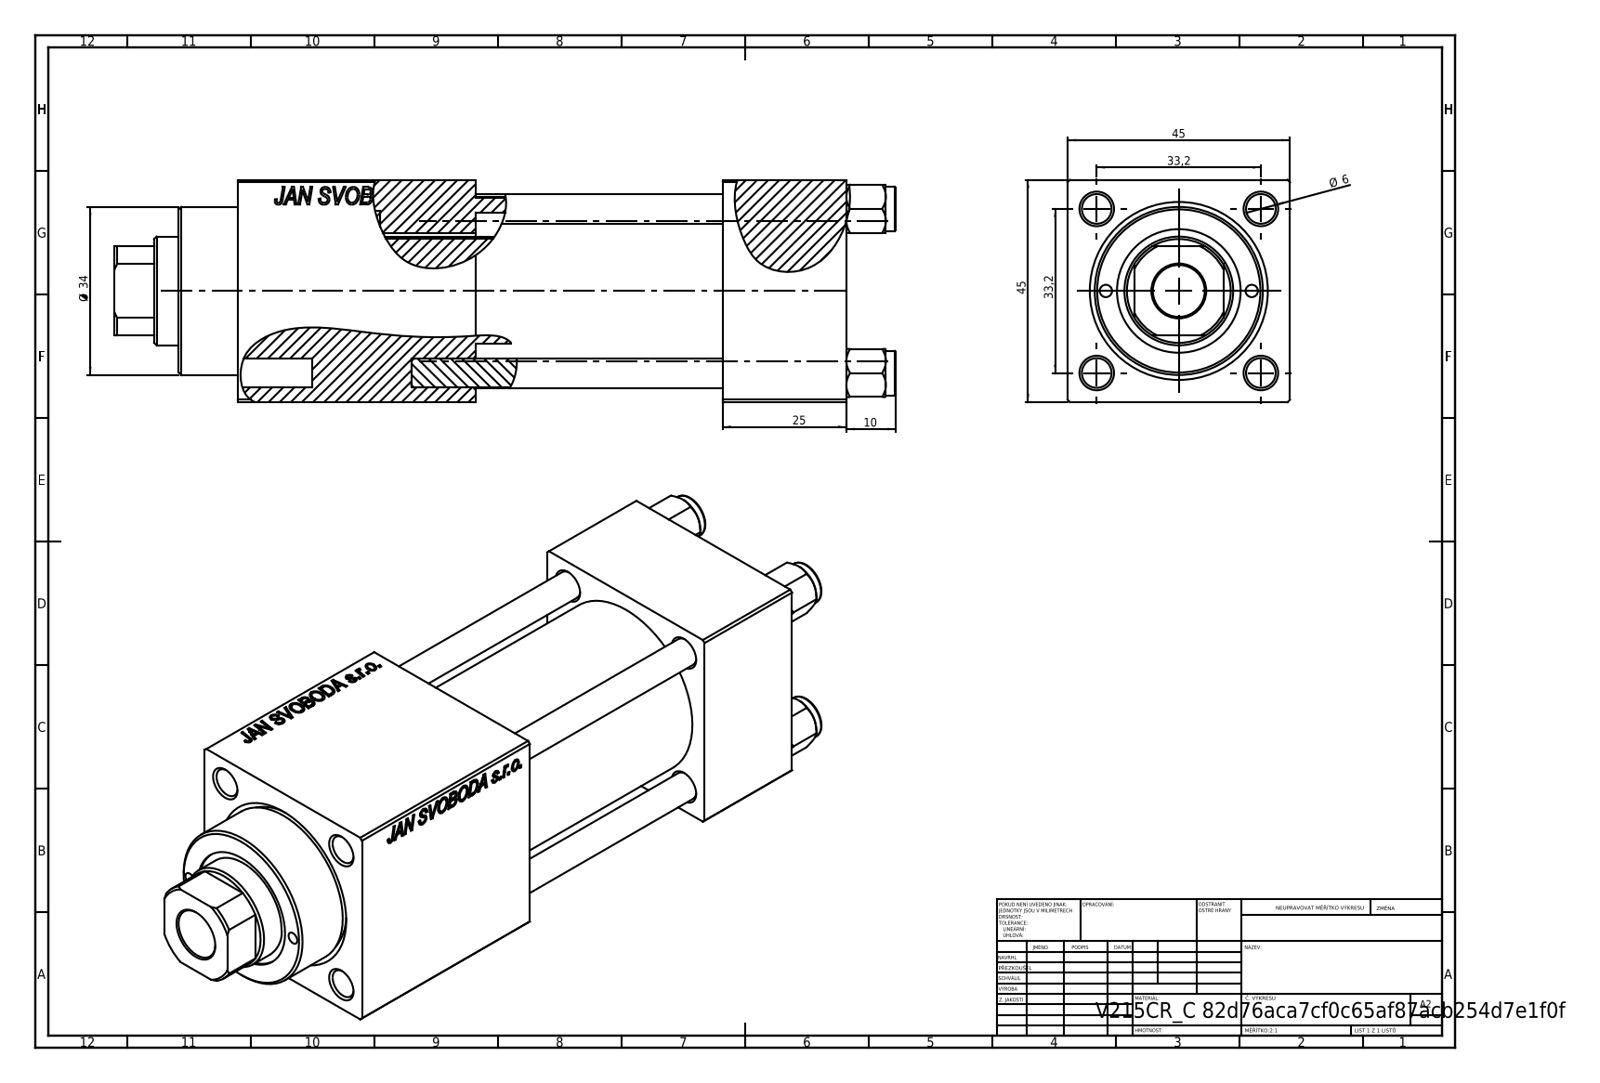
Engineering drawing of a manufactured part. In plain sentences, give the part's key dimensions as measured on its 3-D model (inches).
The part is named "NUT_M5_C; V215CR_C_TYCINKA; V215CR_VCP_C; V215_VC_A (+1 more)". Its 3-D file was written by "SolidWorks 2019 (CONFIG_CONTROL_DESIGN)". It is 11 solids with 1153 faces: 527 planar, 90 cylindrical and 536 other. Overall it measures 6.22 by 1.772 by 1.772 inches. Its volume is 12.8 cubic inches and its surface area 110.9 square inches. Round holes: 4 of diameter 0.236, 2 of diameter 0.098, 2 of diameter 0.276, 2 of diameter 0.518, 2 of diameter 0.787, 1 of diameter 0.413, 1 of diameter 0.866, 1 of diameter 0.945, 1 of diameter 0.984, 1 of diameter 1.26, 1 of diameter 1.299. Round bosses or shafts: 4 of diameter 0.354, 1 of diameter 1.496, 1 of diameter 1.339. Partial cylindrical surfaces (rounded edges, fillets, slot ends): 1 of radius 0.413. The main face-to-face distances are 1.772, 0.984, 1.969, 4.843, 2.953, 3.858, 1.89, 3.713, 2.728, 0.76. The hole center spacings are 0.657, 0.924, 1.307, 1.396, 0.581, 1.848, 1.161, 2.972.
